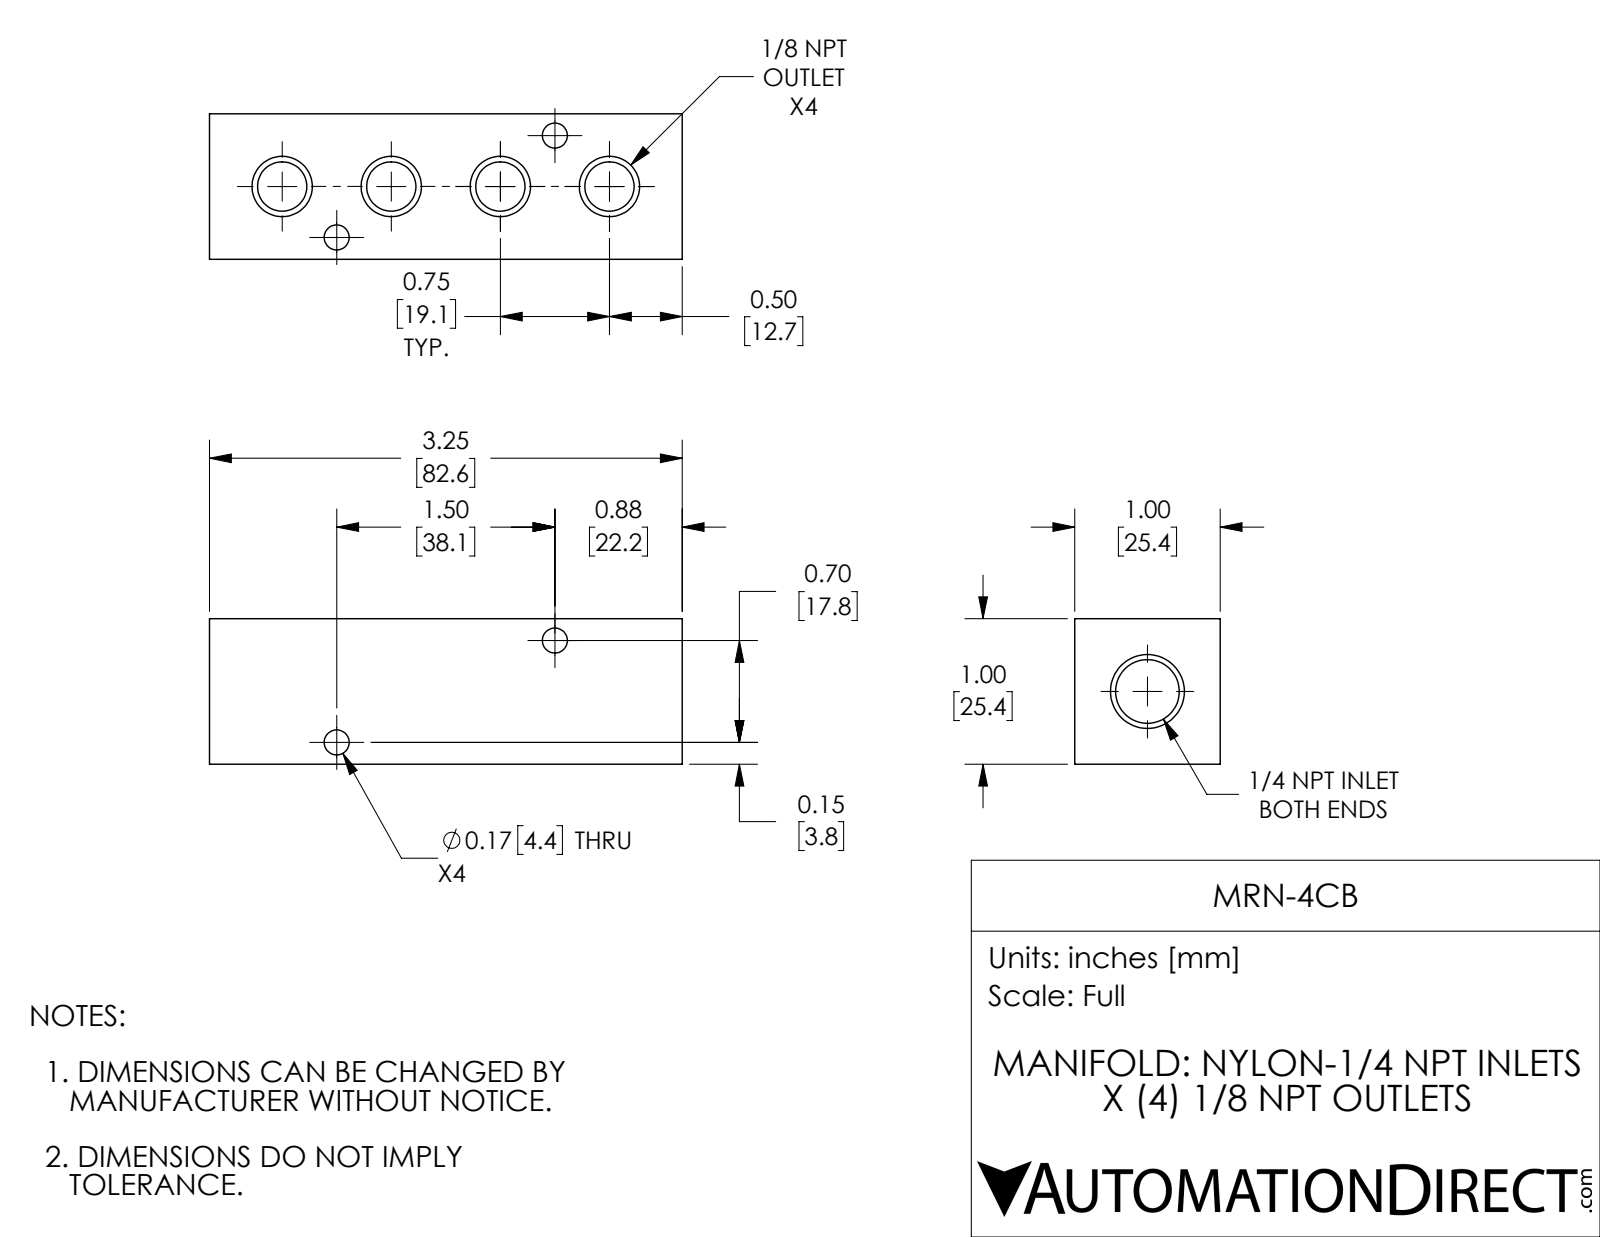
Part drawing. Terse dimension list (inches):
name: MRN-4CB
written by: SolidWorks 2018 (AUTOMOTIVE_DESIGN)
unit: in
bodies: 1 solid, 44 faces (6 planar, 26 cylindrical, 12 other)
size: 3.25 × 1 × 1
volume: 2.561 in³; area: 21.37 in²
holes: 4× ⌀0.172, 4× ⌀0.339, 1× ⌀0.438
face distances: 1, 3.25
hole spacings: 0.513, 0.75, 1.178, 1.5, 1.656, 1.907, 2.25
